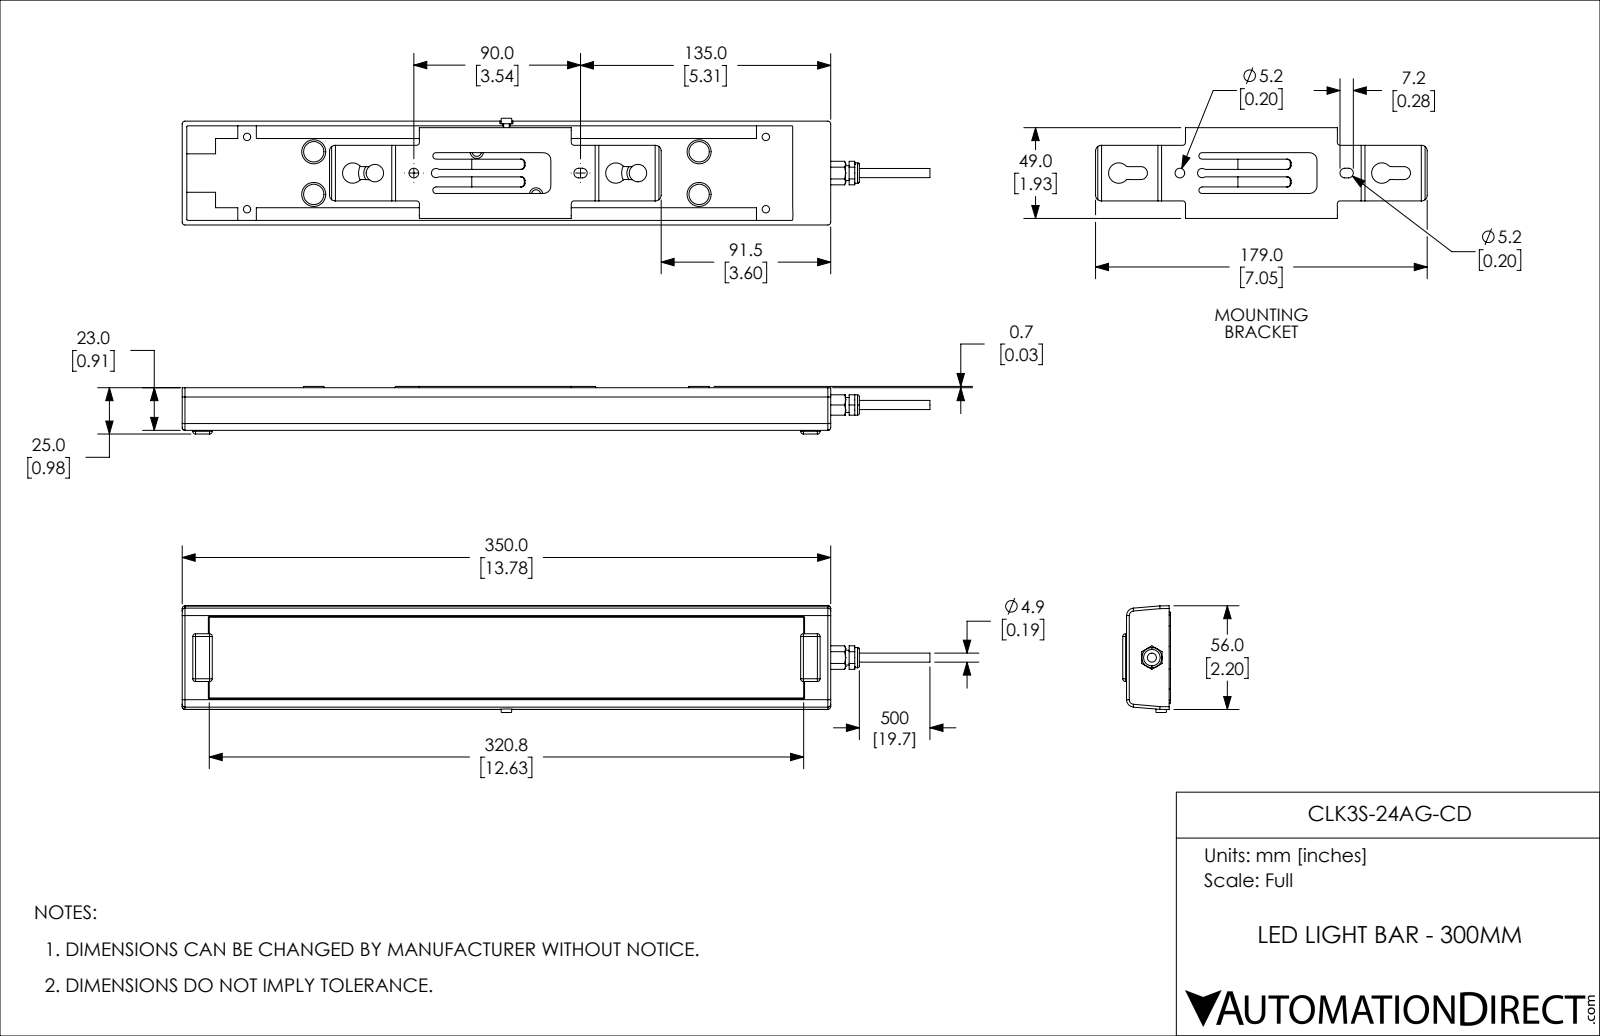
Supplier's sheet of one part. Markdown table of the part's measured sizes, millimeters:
| quantity | value |
| --- | --- |
| part name | CLK3S-24AG-CD |
| STEP written by | SolidWorks 2018 (AUTOMOTIVE_DESIGN) |
| units | millimeters |
| bodies | 3 solids, 274 faces (124 planar, 75 cylindrical, 75 other) |
| overall size | 403.6 × 57.6 × 25.7 |
| volume | 321 400 mm³ |
| surface area | 94 320 mm² |
| round holes (diameter × count) | 4 × 4, 3 × 1, 5.2 × 1 |
| round bosses / shafts (diameter × count) | 11 × 5, 13 × 4, 9.4 × 2, 6.5 × 2, 8 × 1, 4.9 × 1 |
| partial cylindrical surfaces (radius × count) | 1.5 × 20, 2 × 4, 2.6 × 2, 4 × 2 |
| main face-to-face distances | 17.7, 1.5, 6.8, 44.2, 10.3, 7.4, 51, 6, 16.3, 23.7 |
| hole center spacings | 39, 92.1, 191, 280, 282.7 |
